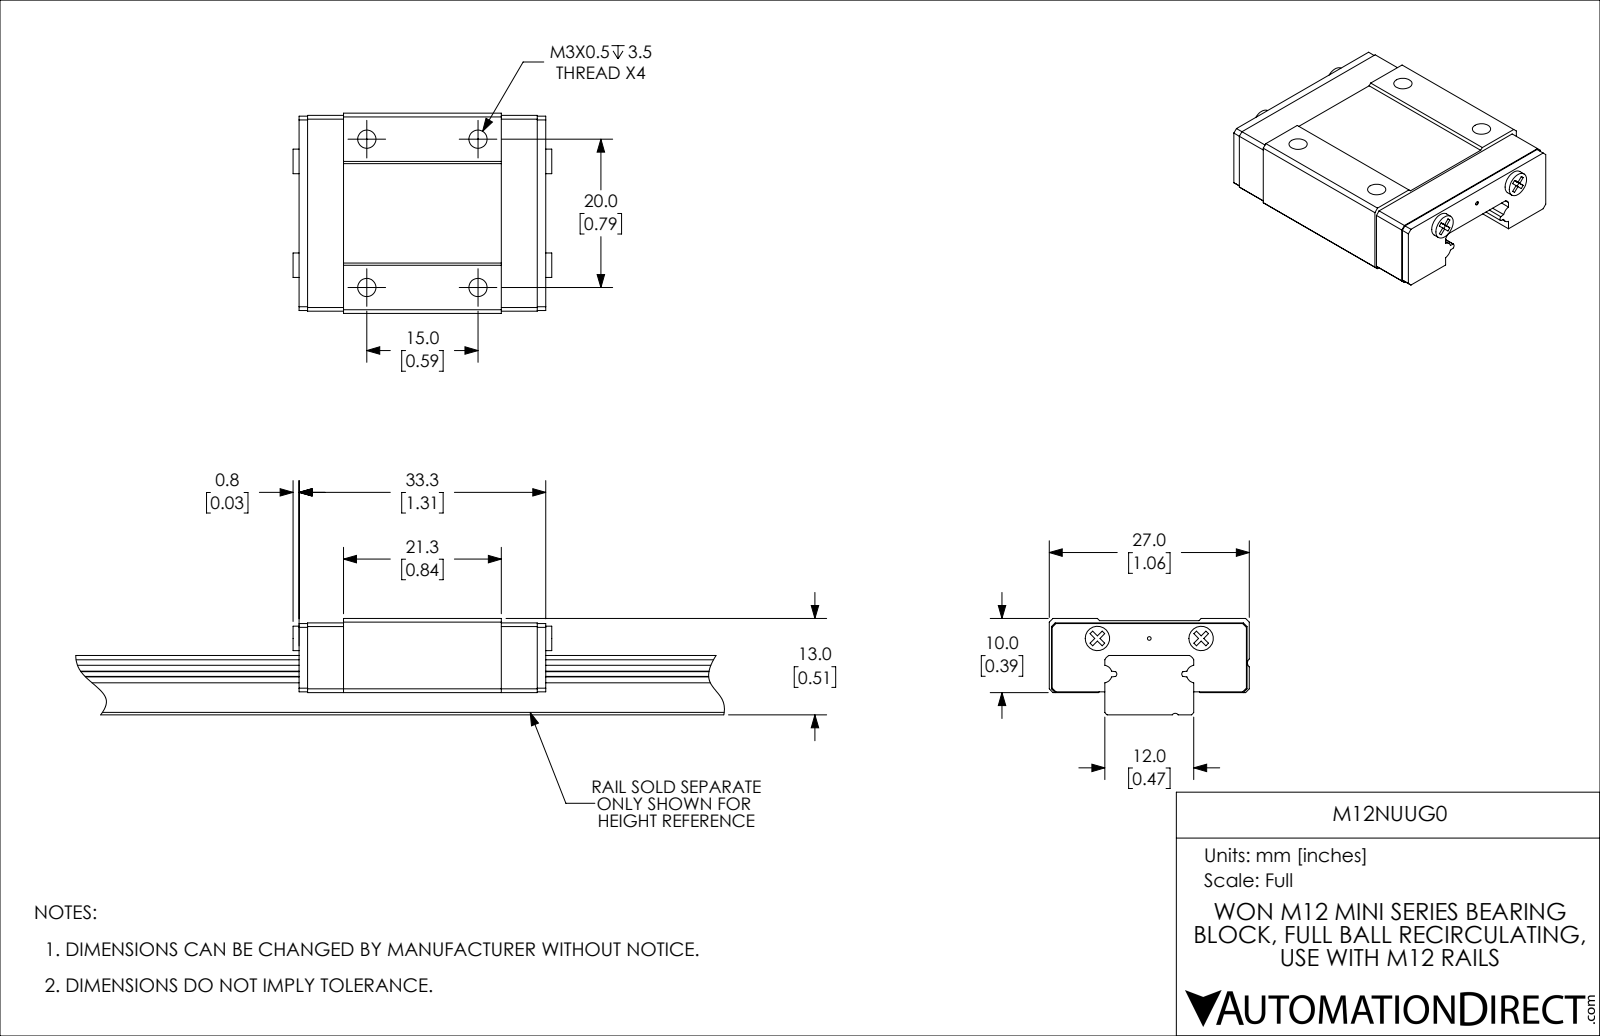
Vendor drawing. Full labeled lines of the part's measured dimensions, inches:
Part name (STEP PRODUCT): M12NUUG0
STEP written by: SolidWorks 2019 (CONFIG_CONTROL_DESIGN)
Units: inches
Bodies: 1 solid, 156 faces (119 planar, 29 cylindrical, 8 other)
Overall size (bounding box): 1.374 × 1.063 × 0.394
Volume: 0.409 in³ · Surface area: 5.329 in²
Round holes (diameter × count): ⌀0.097 ×4, ⌀0.02 ×1
Round bosses / shafts (diameter × count): ⌀0.13 ×2
Partial cylindrical surfaces — rounded edges, fillets, slot ends (radius × count): R0.017 ×2, R0.045 ×2, R0.047 ×2, R0.028 ×1
Main face-to-face distances: 0.197, 0.382, 0.185, 0.37, 0.173, 0.394, 0.024, 1.311, 1.063, 1.051
Hole centre spacings: 0.591, 0.787, 0.984
